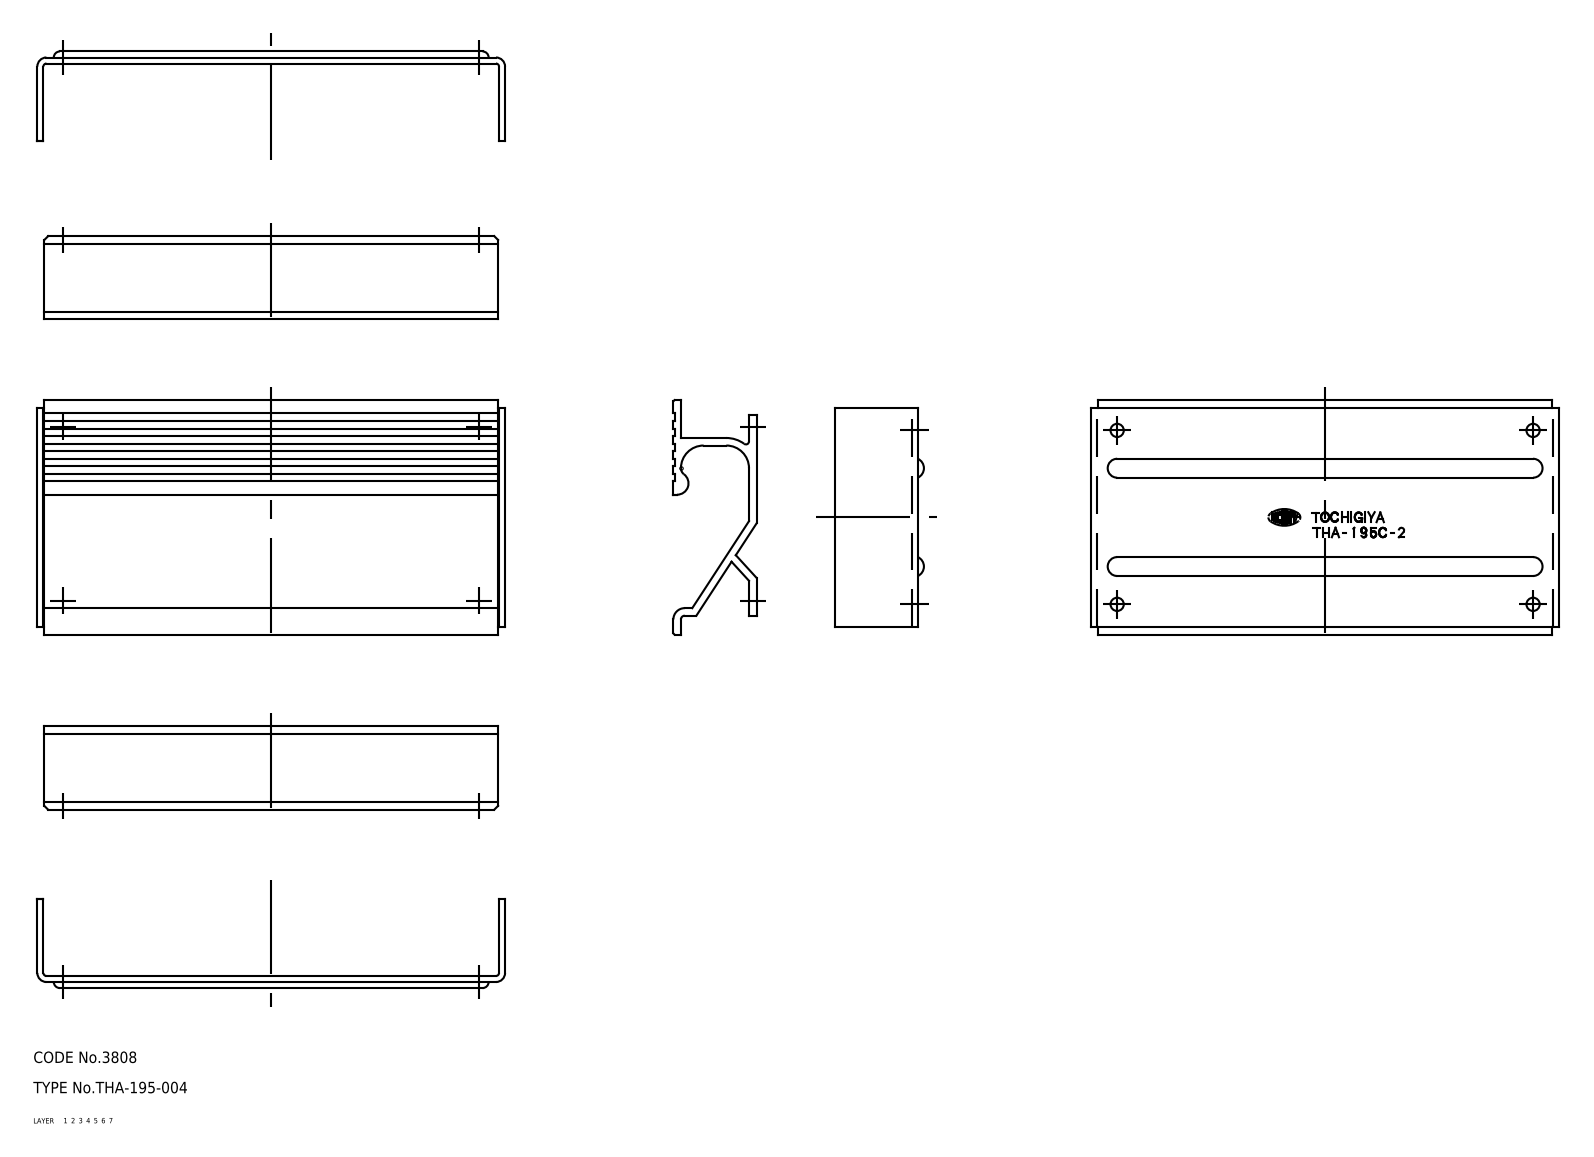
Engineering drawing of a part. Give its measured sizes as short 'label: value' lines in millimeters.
name: pull; bracket; THA_195_004_2986_36
written by: CADfix (AUTOMOTIVE_DESIGN)
unit: mm
bodies: 2 solids, 115 faces (0 planar, 0 cylindrical, 115 other)
size: 123.7 × 62 × 25.2
volume: 48 588 mm³; area: 51 304 mm²
